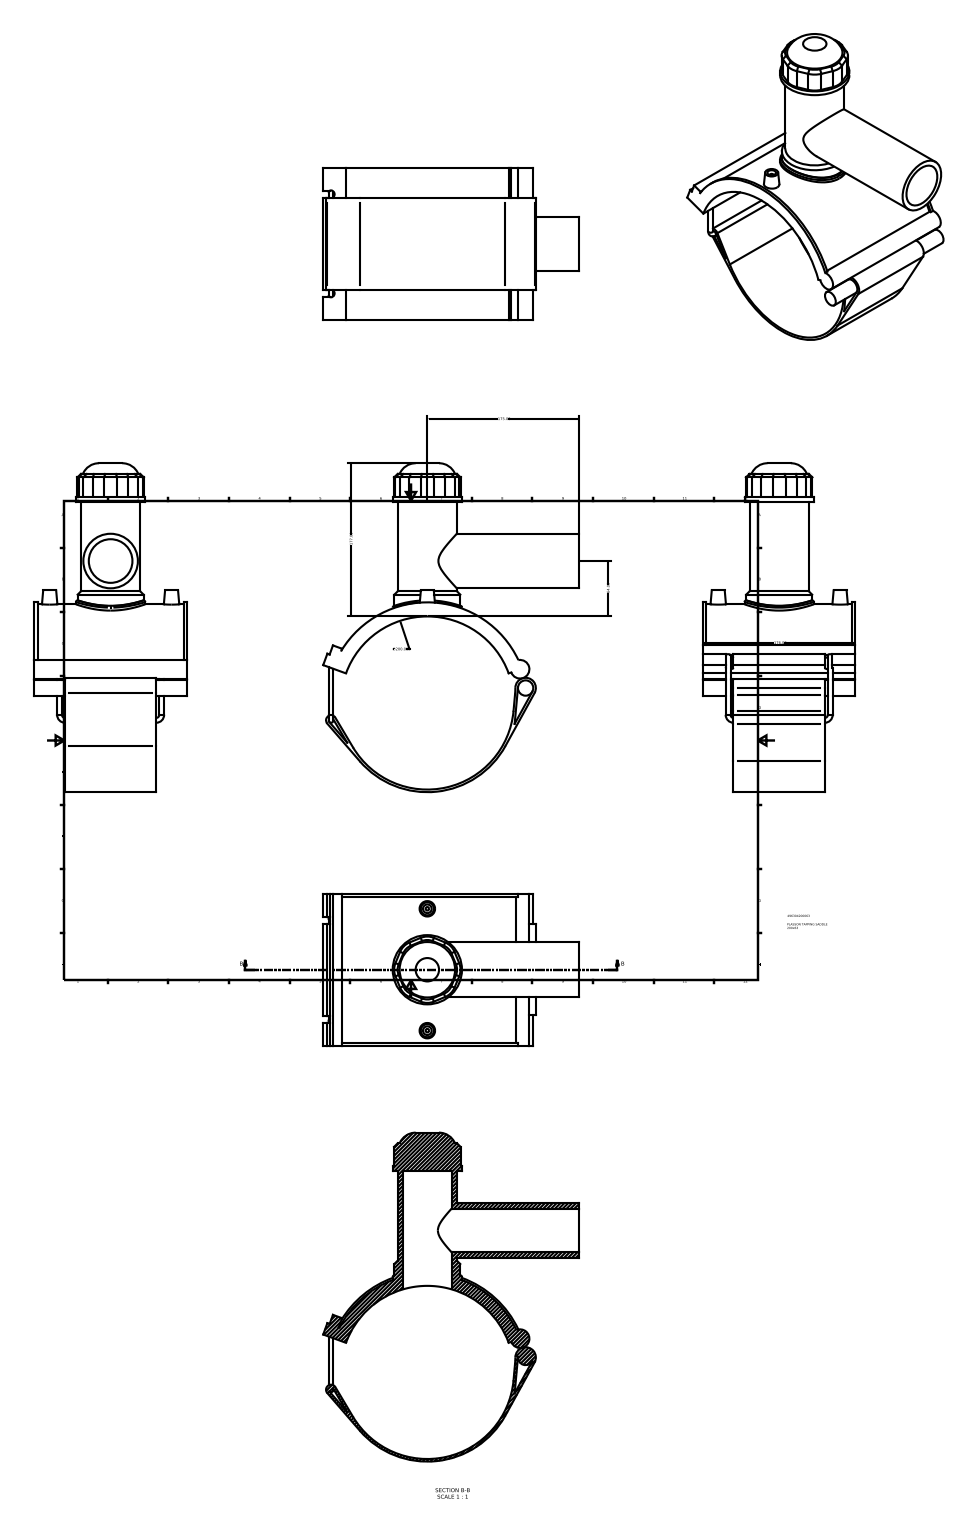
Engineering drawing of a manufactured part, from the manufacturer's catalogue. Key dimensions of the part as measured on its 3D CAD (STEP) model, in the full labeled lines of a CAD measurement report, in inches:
Part name (STEP PRODUCT): 496304200063
STEP written by: Autodesk Inventor 2015 (AUTOMOTIVE_DESIGN)
Units: inches
Bodies: 1 solid, 121 faces (68 planar, 38 cylindrical, 15 other)
Overall size (bounding box): 14.961 × 11.625 × 6.929
Volume: 85.49 in³ · Surface area: 524.1 in²
Round holes (diameter × count): ⌀0.394 ×2, ⌀1.984 ×1, ⌀2.205 ×1
Round bosses / shafts (diameter × count): ⌀0.22 ×2, ⌀0.157 ×2, ⌀3.15 ×1, ⌀2.992 ×1, ⌀2.677 ×1, ⌀2.48 ×1, ⌀0.696 ×1
Partial cylindrical surfaces — rounded edges, fillets, slot ends (radius × count): R0.787 ×8, R0.165 ×2, R3.937 ×2, R0.11 ×1, R0.228 ×1, R0.424 ×1, R0.467 ×1, R4.055 ×1
Main face-to-face distances: 0.118, 6.929, 0.119, 1.386, 5.543, 0.441, 0.551, 0.106, 0.993, 0.11
Hole centre spacings: 2.772, 5.543
